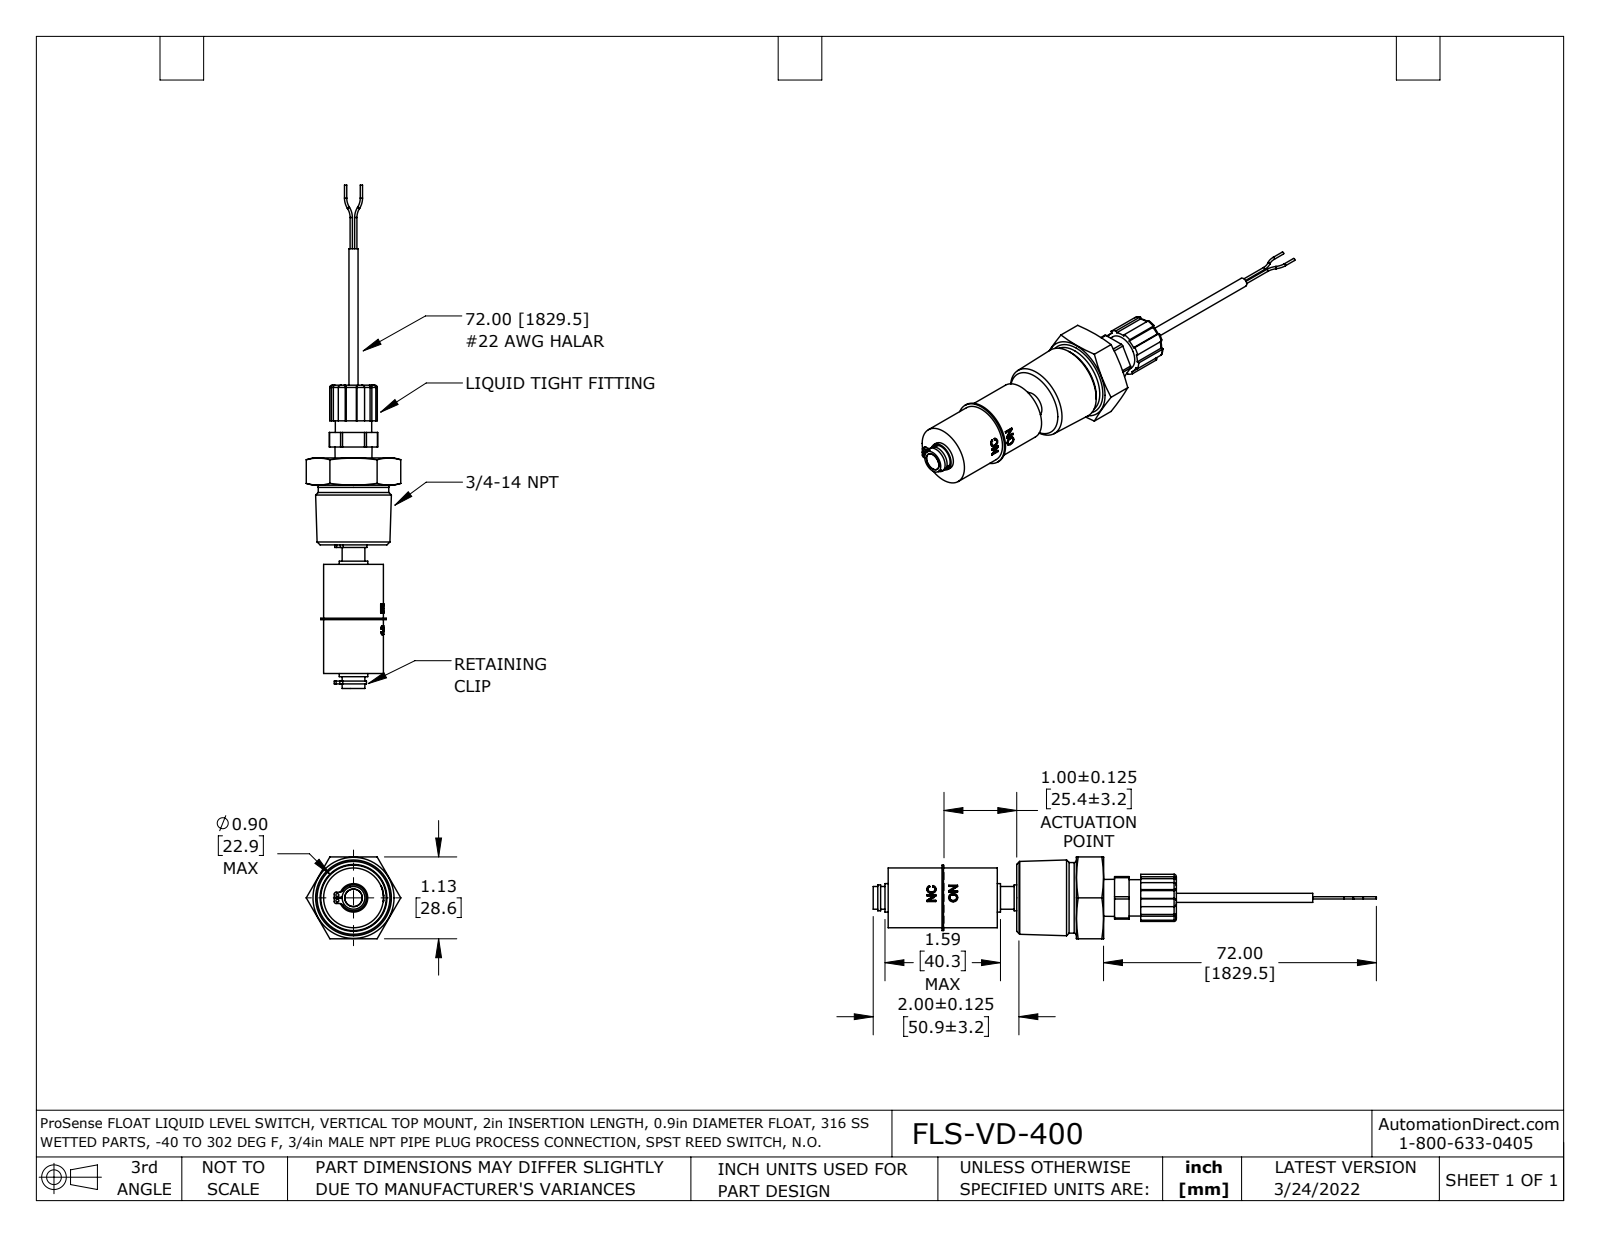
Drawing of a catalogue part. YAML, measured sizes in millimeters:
part_name: "ADM4169-1 nc coord fxt"
step_written_by: "SolidWorks 2021 (AUTOMOTIVE_DESIGN)"
units: millimeters
bodies: {solids: 9, faces: 263, planar: 85, cylindrical: 116, other: 62}
overall_size: [175.7, 33, 28.6]
volume: 32760
surface_area: 16170
round_holes:
  - {diameter: 1, count: 4}
  - {diameter: 7.4, count: 2}
  - {diameter: 6.2, count: 1}
  - {diameter: 7.1, count: 1}
  - {diameter: 7.9, count: 1}
  - {diameter: 8, count: 1}
  - {diameter: 8.9, count: 1}
round_bosses_or_shafts:
  - {diameter: 0.8, count: 6}
  - {diameter: 9, count: 2}
  - {diameter: 24.6, count: 1}
  - {diameter: 22.9, count: 1}
  - {diameter: 20.9, count: 1}
  - {diameter: 12.7, count: 1}
  - {diameter: 10, count: 1}
  - {diameter: 8.4, count: 1}
partial_cylinders:
  - {radius: 0.8, count: 16}
  - {radius: 0.7, count: 4}
  - {radius: 1.2, count: 4}
  - {radius: 7.6, count: 1}
  - {radius: 8.3, count: 1}
  - {radius: 10.6, count: 1}
face_to_face_distances: [28.6, 30.4, 37.2, 75.3, 6.8, 44.9, 38.1, 6.9, 21.7, 19.3]
hole_center_spacings: [5.6, 2, 2, 5.4, 5.7]
